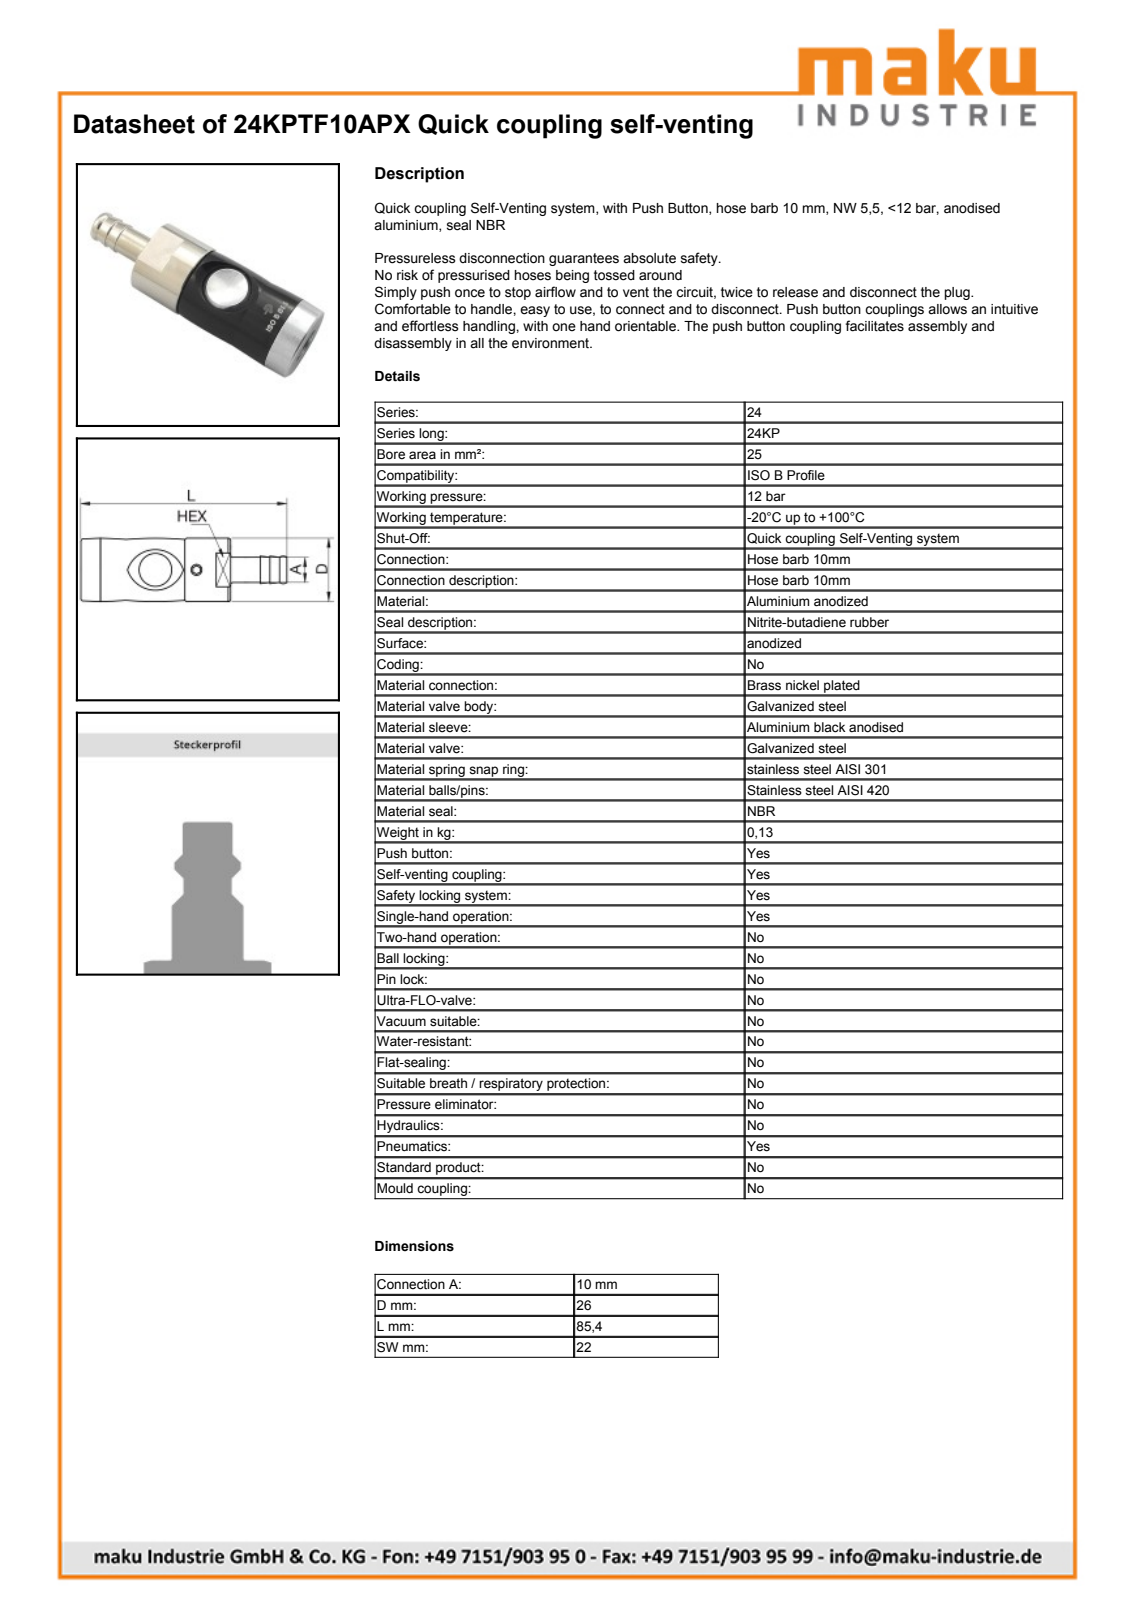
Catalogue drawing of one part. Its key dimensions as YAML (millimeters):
step_written_by: "Autodesk Inventor 2019 (CONFIG_CONTROL_DESIGN)"
units: millimeters
bodies: {solids: 39, faces: 218, planar: 63, cylindrical: 67, other: 88}
overall_size: [85.4, 26, 26]
volume: 40174
surface_area: 24763
round_holes:
  - {diameter: 12.4, count: 2}
  - {diameter: 3.5, count: 1}
  - {diameter: 6.5, count: 1}
  - {diameter: 8, count: 1}
  - {diameter: 9.6, count: 1}
  - {diameter: 9.65, count: 1}
  - {diameter: 10.6, count: 1}
  - {diameter: 12, count: 1}
  - {diameter: 12.25, count: 1}
  - {diameter: 13.6, count: 1}
  - {diameter: 15, count: 1}
  - {diameter: 15.91, count: 1}
round_bosses_or_shafts:
  - {diameter: 26, count: 1}
  - {diameter: 22.4, count: 1}
  - {diameter: 22, count: 1}
  - {diameter: 20.5, count: 1}
  - {diameter: 18.1, count: 1}
  - {diameter: 17.14, count: 1}
  - {diameter: 16.5, count: 1}
  - {diameter: 15.8, count: 1}
partial_cylinders:
  - {radius: 6.2, count: 2}
face_to_face_distances: [43.1, 19, 35, 8.1, 54, 62.1, 1, 2.39, 16.61, 51.61]
hole_center_spacings: [0.6, 0.7, 1.3, 17.05]
